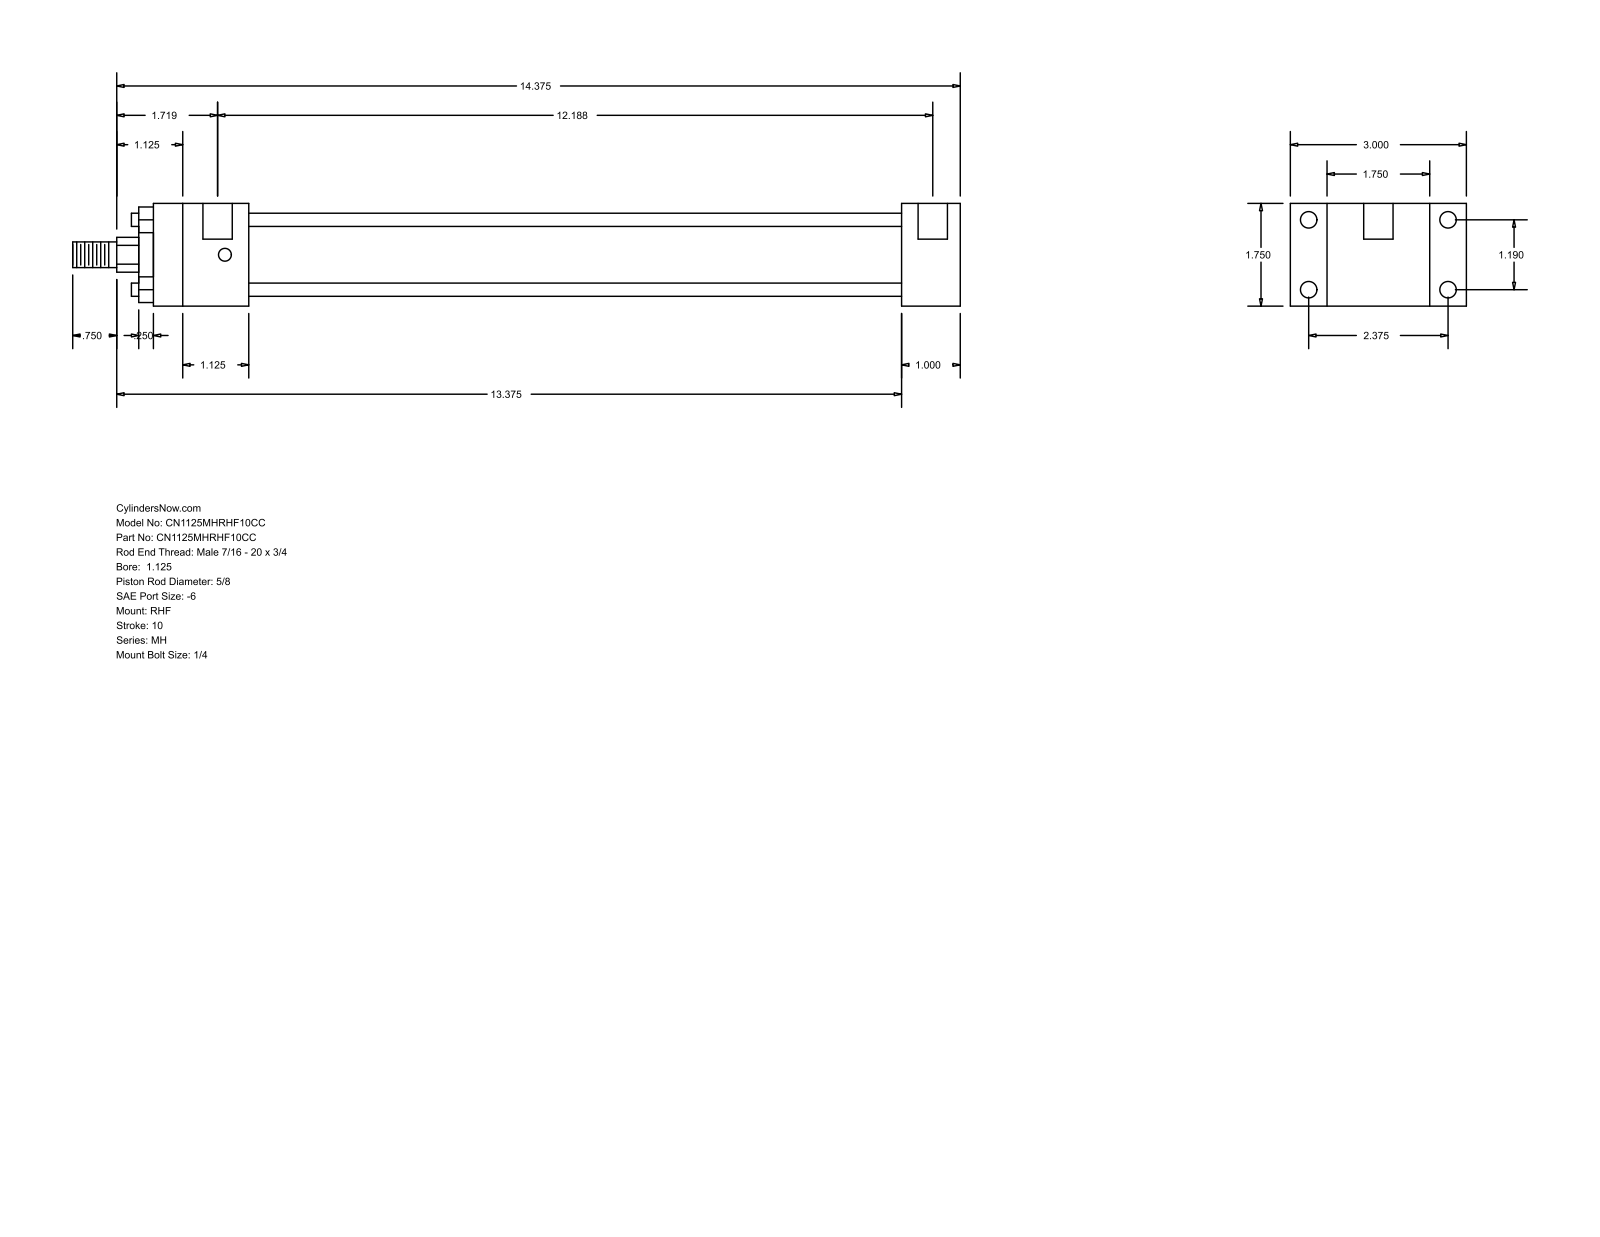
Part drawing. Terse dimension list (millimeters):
name: MH_RHF__0112_0.625
written by: GSSL Pune (CONFIG_CONTROL_DESIGN)
unit: mm
bodies: 0 solids, 88 faces (60 planar, 28 cylindrical, 0 other)
size: 384.18 × 76.2 × 44.45
holes: 4× ⌀5.56, 4× ⌀7.14, 2× ⌀12.7
bosses: 4× ⌀5.71, 1× ⌀34.92, 1× ⌀28.57, 1× ⌀15.88, 1× ⌀11.11
rounds: 1× R7.54
face distances: 44.46, 15.87, 60.33, 25.39, 76.2, 282.58, 307.97, 41.27, 323.85, 349.24
hole spacings: 30.22, 60.32, 67.47, 306.39, 3.17, 309.56
